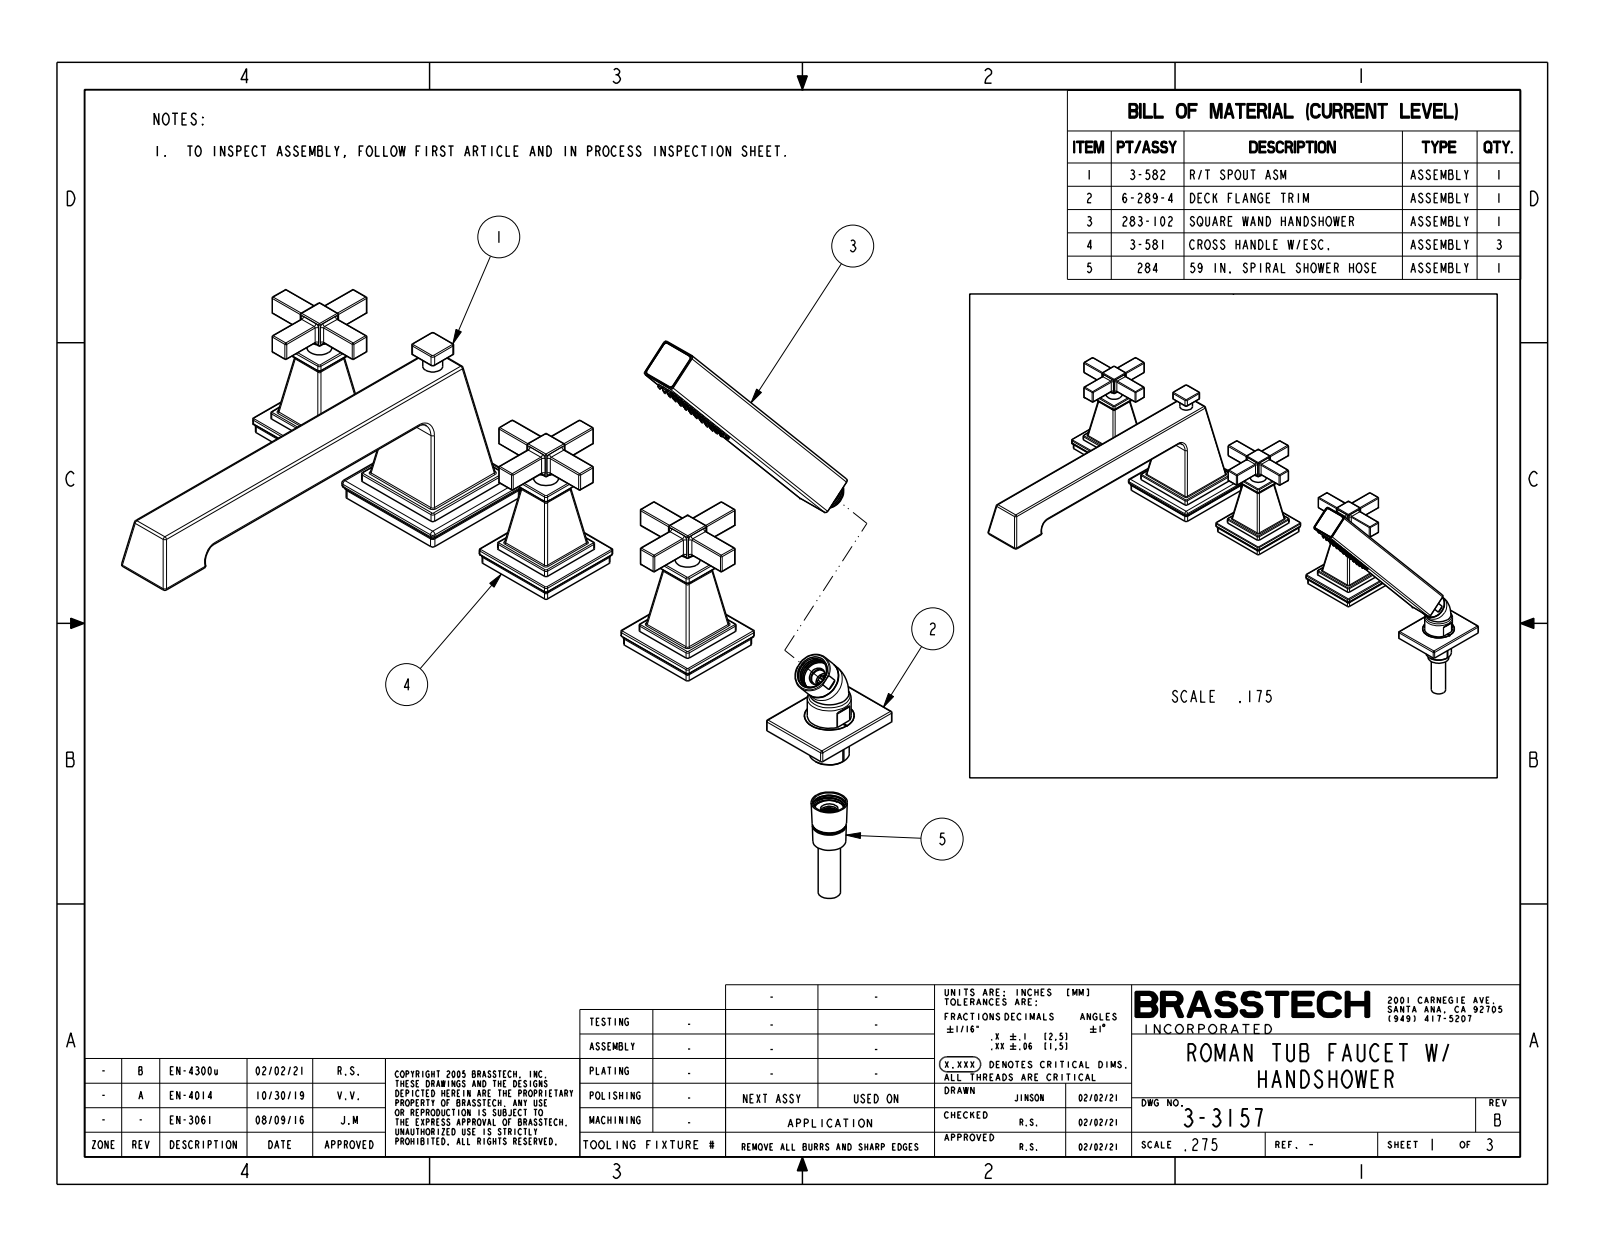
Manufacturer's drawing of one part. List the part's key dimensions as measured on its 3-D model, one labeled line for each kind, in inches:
Part name (STEP PRODUCT): 3-3157
STEP written by: CREO PARAMETRIC BY PTC INC, 2018400 (CONFIG_CONTROL_DESIGN)
Units: inches
Bodies: 5 solids, 1822 faces (282 planar, 612 cylindrical, 928 other)
Overall size (bounding box): 20.422 × 11.863 × 8.772
Volume: 61.15 in³ · Surface area: 258 in²
Round holes (diameter × count): ⌀0.14 ×44, ⌀0.835 ×1
Round bosses / shafts (diameter × count): ⌀0.625 ×3, ⌀0.506 ×3, ⌀1.095 ×1, ⌀0.98 ×1, ⌀0.975 ×1, ⌀0.825 ×1, ⌀0.5 ×1
Partial cylindrical surfaces — rounded edges, fillets, slot ends (radius × count): R0.03 ×140, R0.06 ×100, R0.062 ×20, R0.09 ×20, R0.01 ×16, R0.078 ×16, R0.23 ×12, R0.033 ×8
Main face-to-face distances: 0.93, 0.5, 4.009, 0.41, 3.599, 3.079, 2.669, 1, 0.474, 1
Hole centre spacings: 0.336, 0.17, 0.447, 0.672, 0.604, 0.29, 0.87, 0.887
